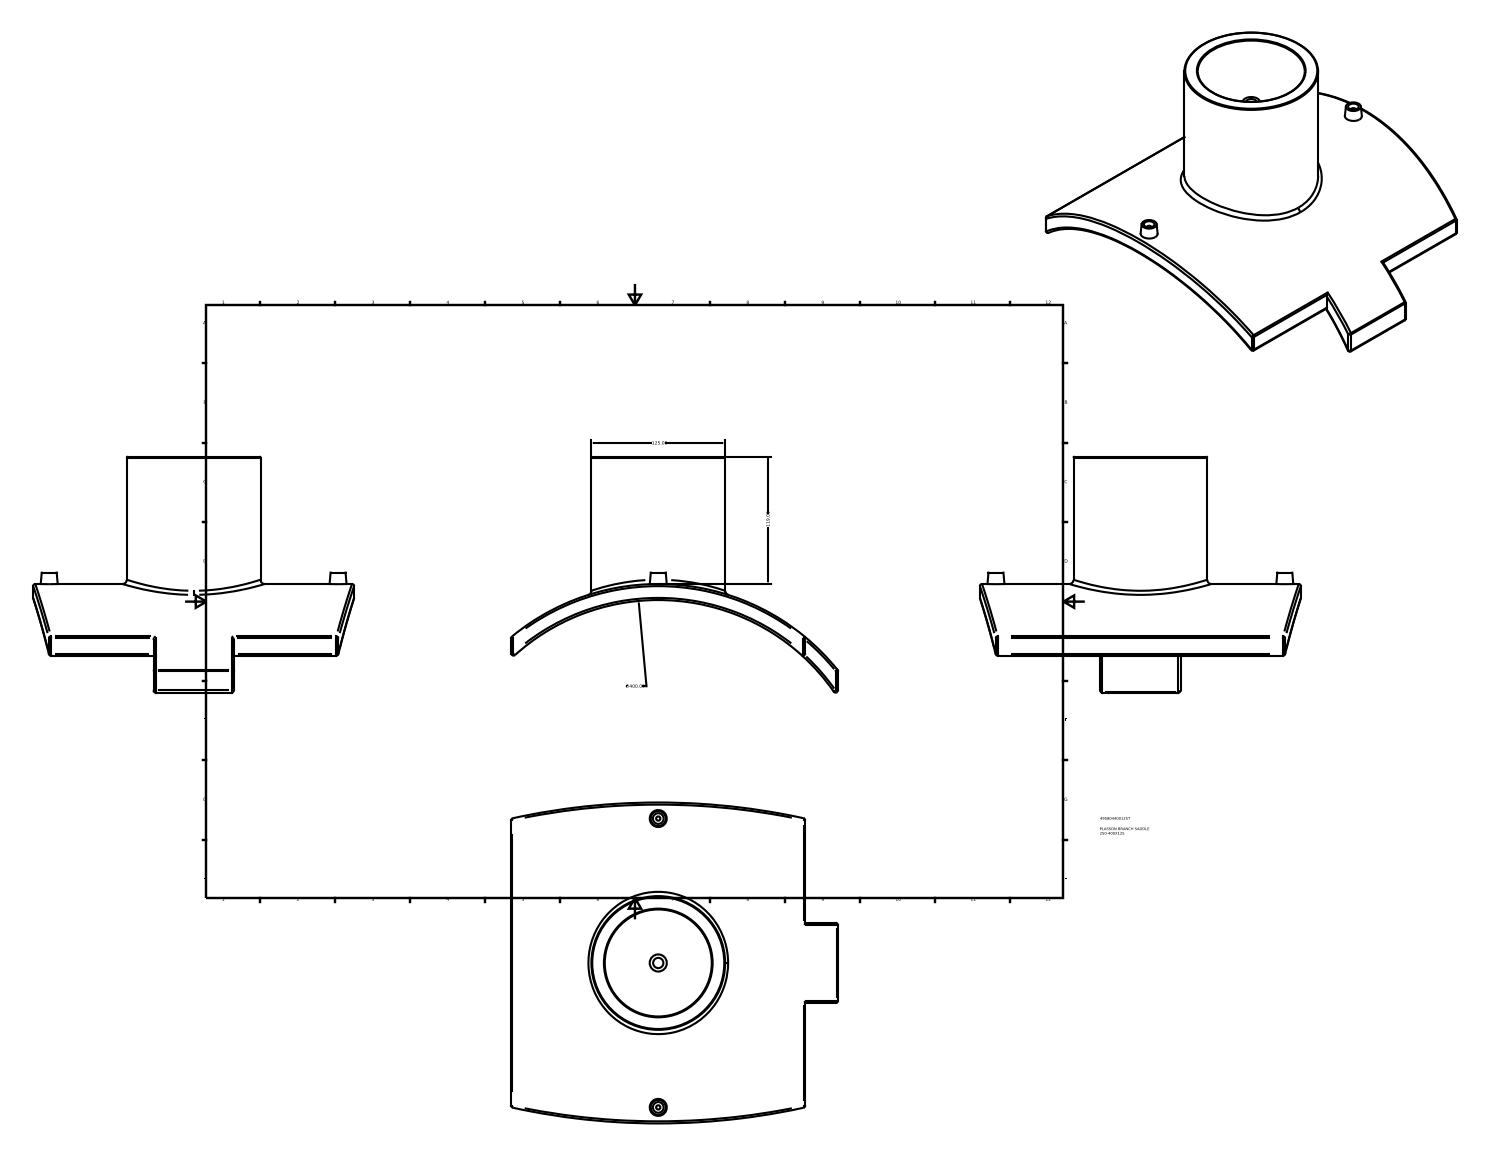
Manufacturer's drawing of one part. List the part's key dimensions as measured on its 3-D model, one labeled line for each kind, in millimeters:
Part name (STEP PRODUCT): 495804400125T
STEP written by: Autodesk Inventor 2015 (AUTOMOTIVE_DESIGN)
Units: millimetres
Bodies: 1 solid, 66 faces (14 planar, 27 cylindrical, 25 other)
Overall size (bounding box): 305 × 300 × 220.54
Volume: 1 904 000 mm³ · Surface area: 293 230 mm²
Round holes (diameter × count): ⌀10 ×2, ⌀9.6 ×1, ⌀100 ×1
Round bosses / shafts (diameter × count): ⌀4 ×2, ⌀125 ×1, ⌀16 ×1
Partial cylindrical surfaces — rounded edges, fillets, slot ends (radius × count): R2 ×12, R635.42 ×2, R200 ×1, R215 ×1
Main face-to-face distances: 274.5, 305, 30.5, 75, 108.4, 14, 122.4, 86.7, 72.7, 35.7
Hole centre spacings: 135, 270
